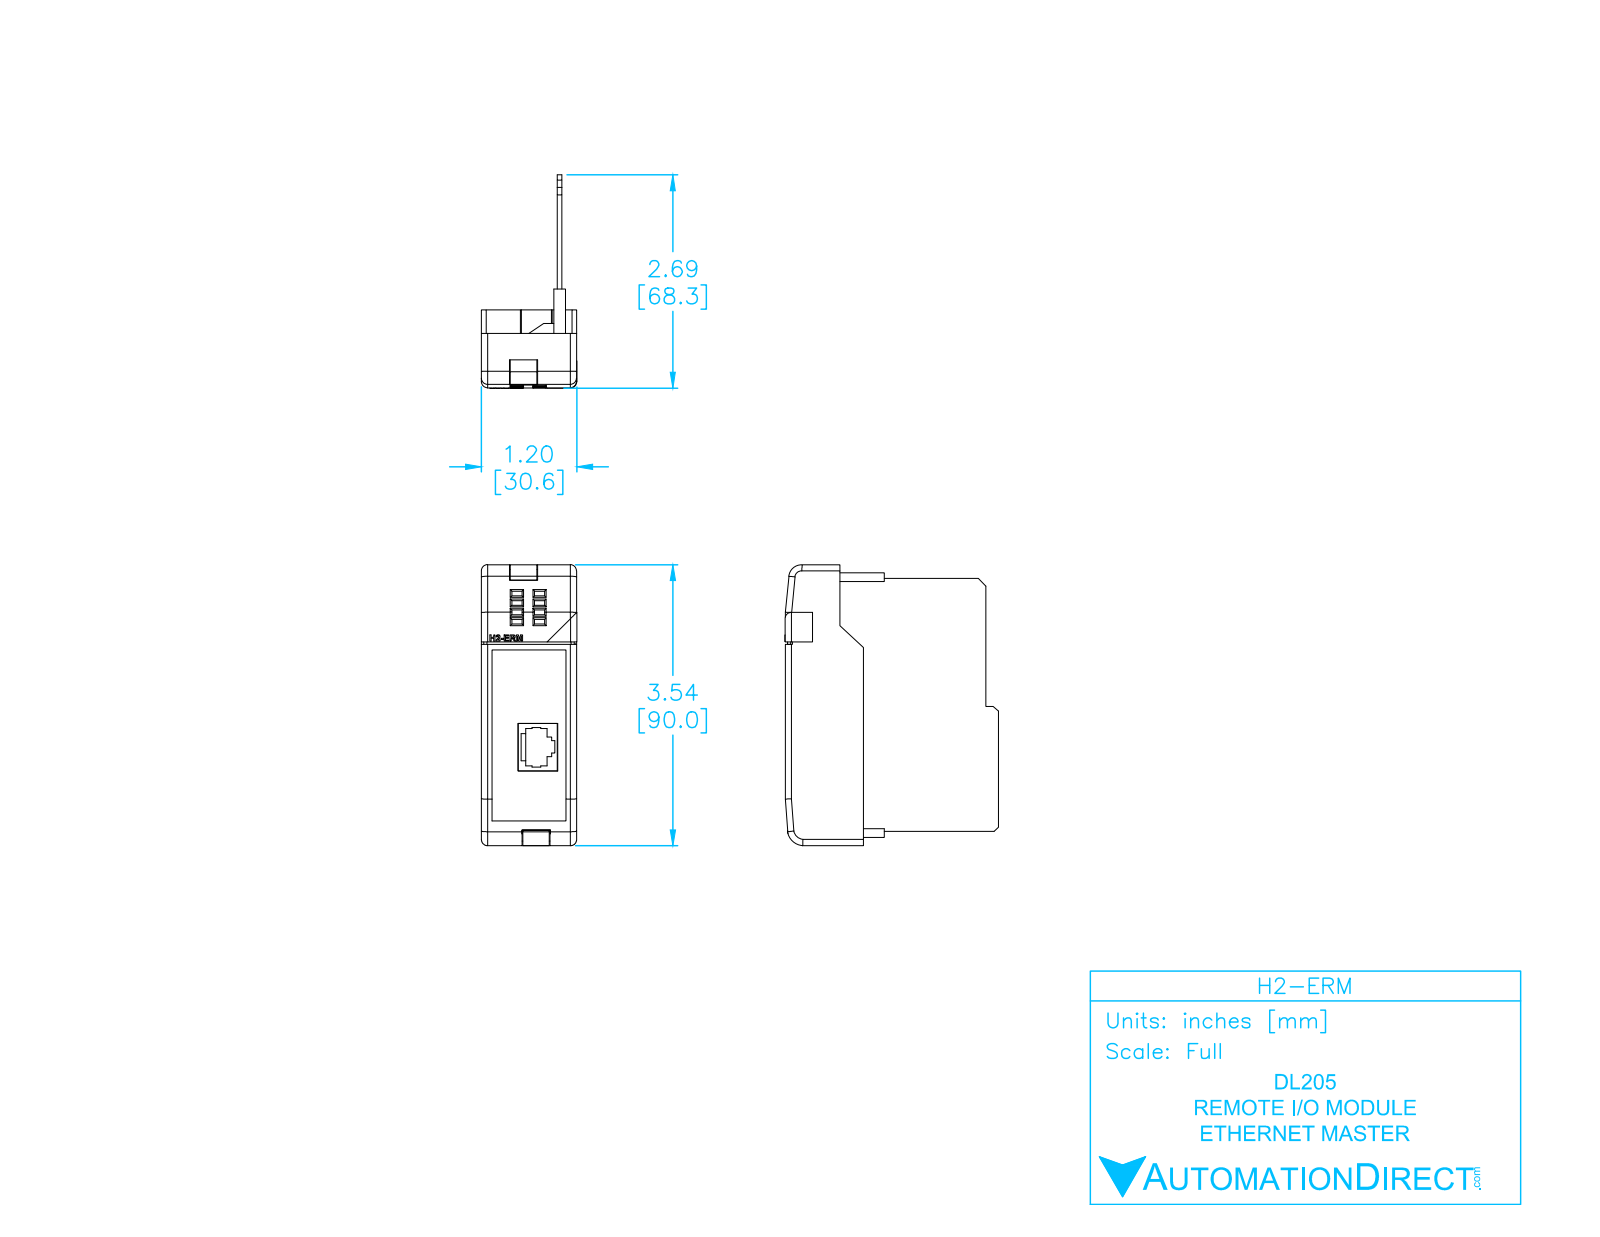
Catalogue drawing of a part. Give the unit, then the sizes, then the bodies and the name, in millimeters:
Units: millimetres
Overall size (bounding box): 90 × 68.38 × 30.55
Partial cylindrical surfaces — rounded edges, fillets, slot ends (radius × count): R0.5 ×29, R2 ×11, R0.25 ×4, R1 ×2, R2.62 ×1, R3.79 ×1, R4.12 ×1, R5.29 ×1
Main face-to-face distances: 1.5, 4.72, 3.22, 6.22, 0.5, 24.28, 29, 25.78, 30.5, 27.5
Volume: 18 926 mm³ · Surface area: 28 848 mm²
Bodies: 2 solids, 376 faces (265 planar, 85 cylindrical, 26 other)
Part name (STEP PRODUCT): H2-ERM_ModuleCase_NEW
STEP written by: SolidWorks 2009 (AUTOMOTIVE_DESIGN)
